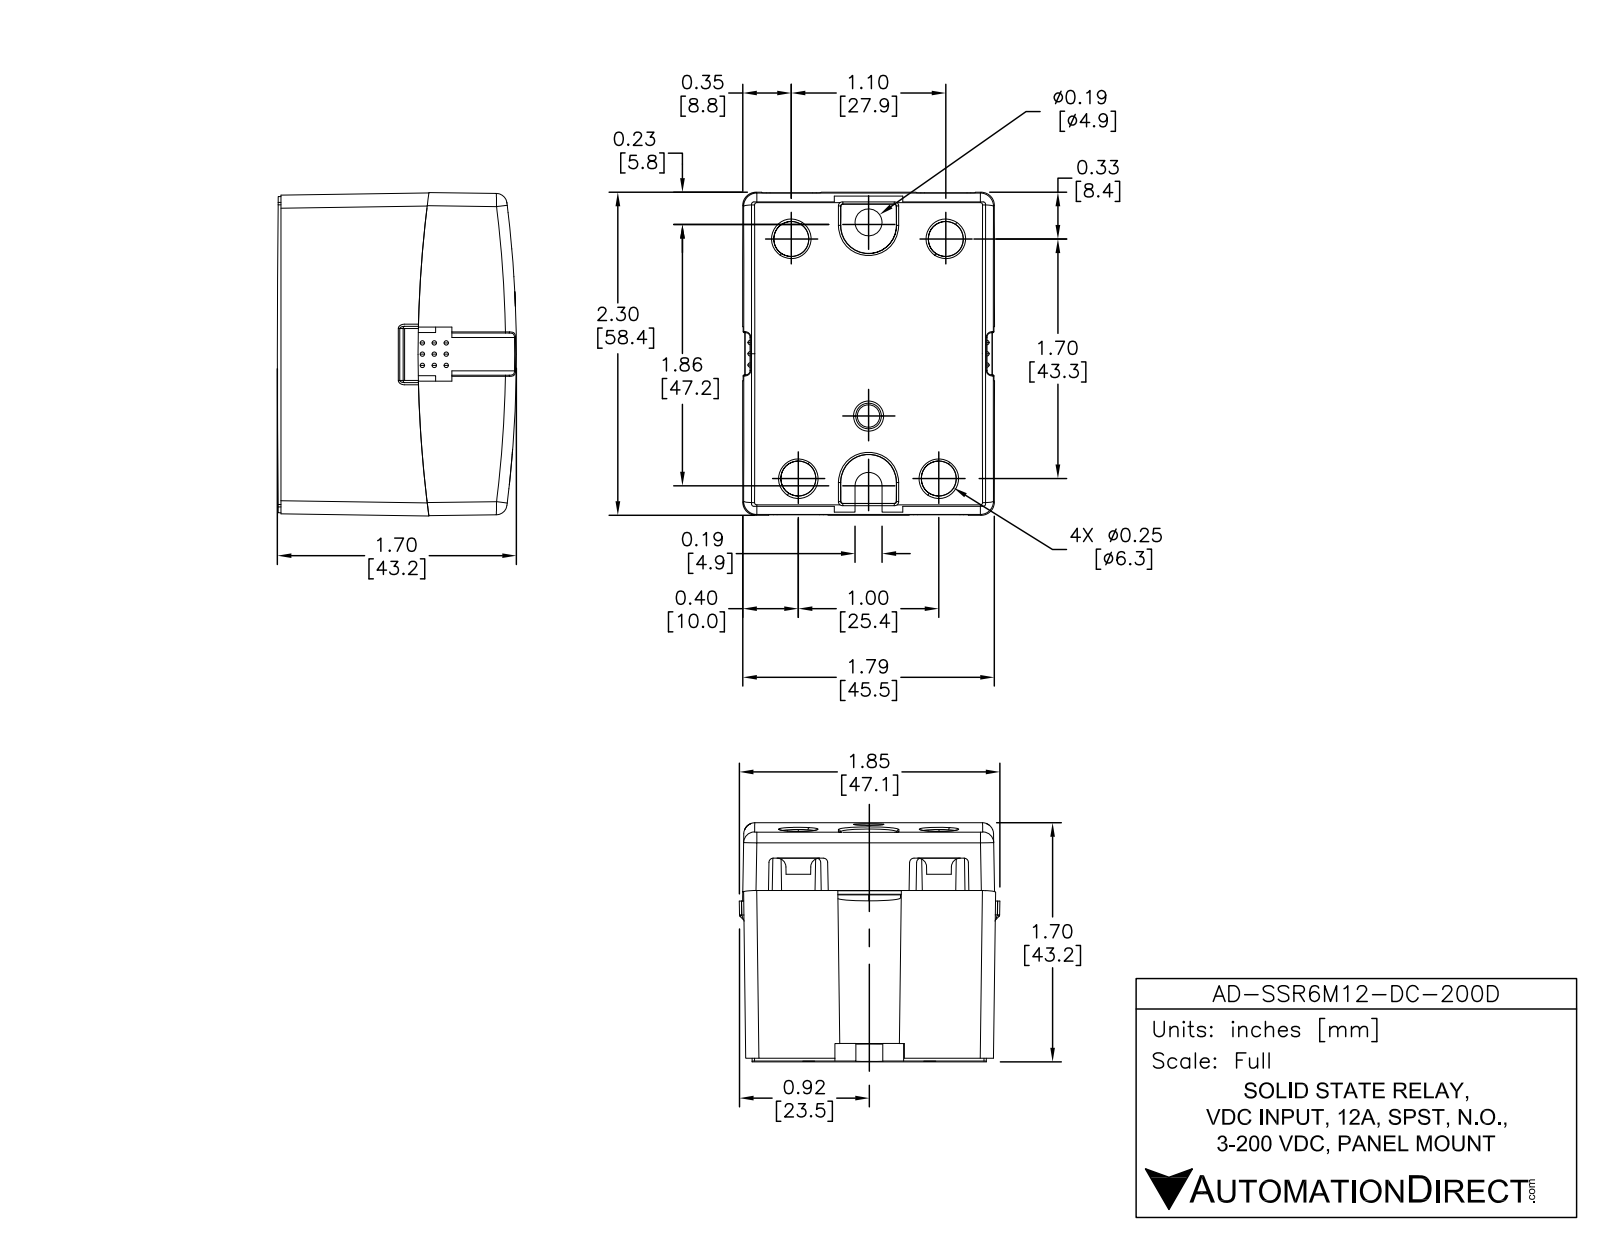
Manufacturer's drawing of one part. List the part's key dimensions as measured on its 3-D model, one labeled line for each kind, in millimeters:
Part name (STEP PRODUCT): AD-SSR6M12-DC-200D
STEP written by: SolidWorks 2013 (AUTOMOTIVE_DESIGN)
Units: millimetres
Bodies: 1 solid, 330 faces (196 planar, 111 cylindrical, 23 other)
Overall size (bounding box): 58.4 × 45.5 × 43.2
Volume: 102 600 mm³ · Surface area: 19 520 mm²
Round holes (diameter × count): ⌀6.4 ×4, ⌀4.8 ×1
Round bosses / shafts (diameter × count): ⌀10.2 ×2, ⌀8.9 ×2, ⌀7.8 ×2, ⌀7.6 ×2, ⌀5.1 ×2, ⌀5.1 ×2
Partial cylindrical surfaces — rounded edges, fillets, slot ends (radius × count): R0.8 ×6, R0.3 ×4, R1 ×2, R4.9 ×2, R2.4 ×1, R12.6 ×1, R12.7 ×1, R13.4 ×1
Main face-to-face distances: 45.5, 58.4, 33, 26.7, 6.4, 1.3, 17, 26.9, 1.9, 56.5
Hole centre spacings: 27.9, 43.2, 51.4, 14.1, 14.3, 47.8, 47.8
